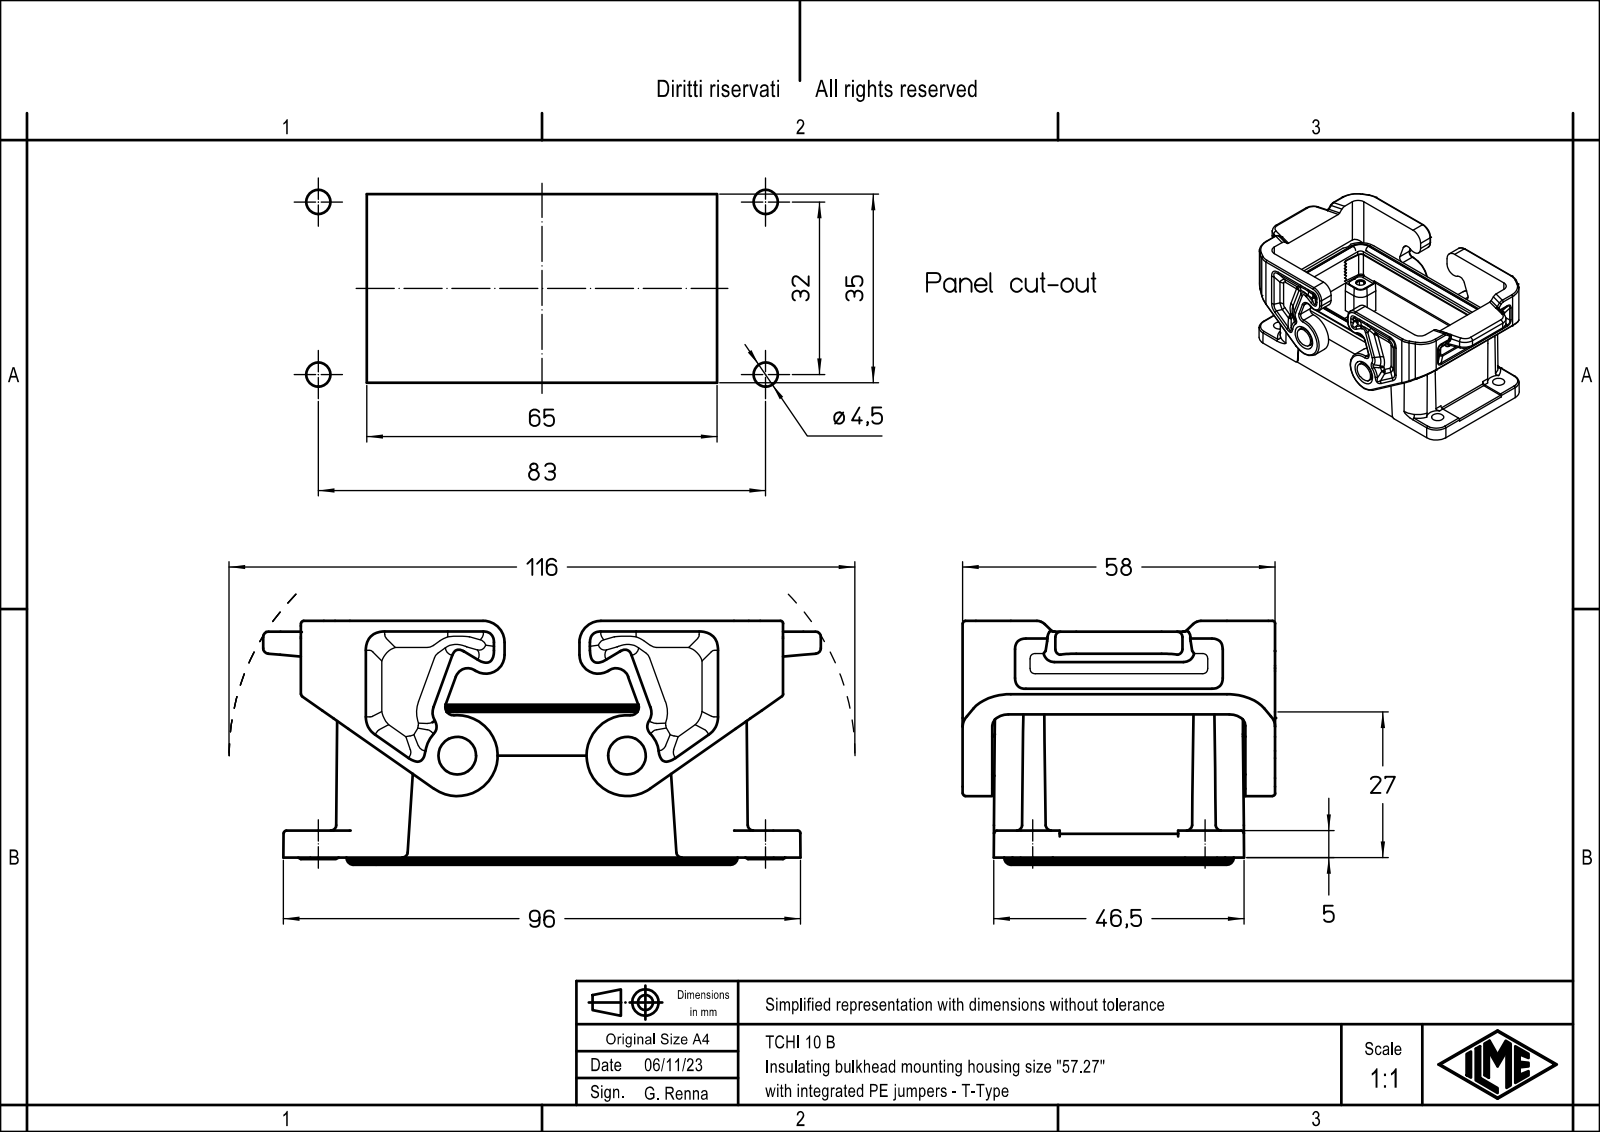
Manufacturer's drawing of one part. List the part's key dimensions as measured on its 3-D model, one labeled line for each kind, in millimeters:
Part name (STEP PRODUCT): TCHI 10 B
STEP written by: Creo Elements/Direct Modeling 20.1B 02-Apr-2019 (C) Parametric Technology GmbH (AUTOMOTIVE_DESIGN)
Units: millimetres
Bodies: 1 solid, 821 faces (404 planar, 249 cylindrical, 168 other)
Overall size (bounding box): 103.5 × 58 × 45.25
Volume: 64 813 mm³ · Surface area: 37 556 mm²
Round holes (diameter × count): ⌀2.5 ×4, ⌀3.5 ×4, ⌀4.5 ×4, ⌀7.2 ×2
Round bosses / shafts (diameter × count): ⌀4.8 ×4, ⌀7 ×2
Partial cylindrical surfaces — rounded edges, fillets, slot ends (radius × count): R1 ×25, R1.3 ×20, R1.5 ×18, R2 ×16, R3 ×12, R5.5 ×12, R5 ×8, R6 ×8
Main face-to-face distances: 40.6, 5.5, 52.5, 47, 40.4, 70.61, 45.9, 6.3, 46.2, 11.8
Hole centre spacings: 13.24, 32.24, 70.04, 75.96, 27, 32, 57, 63.07
